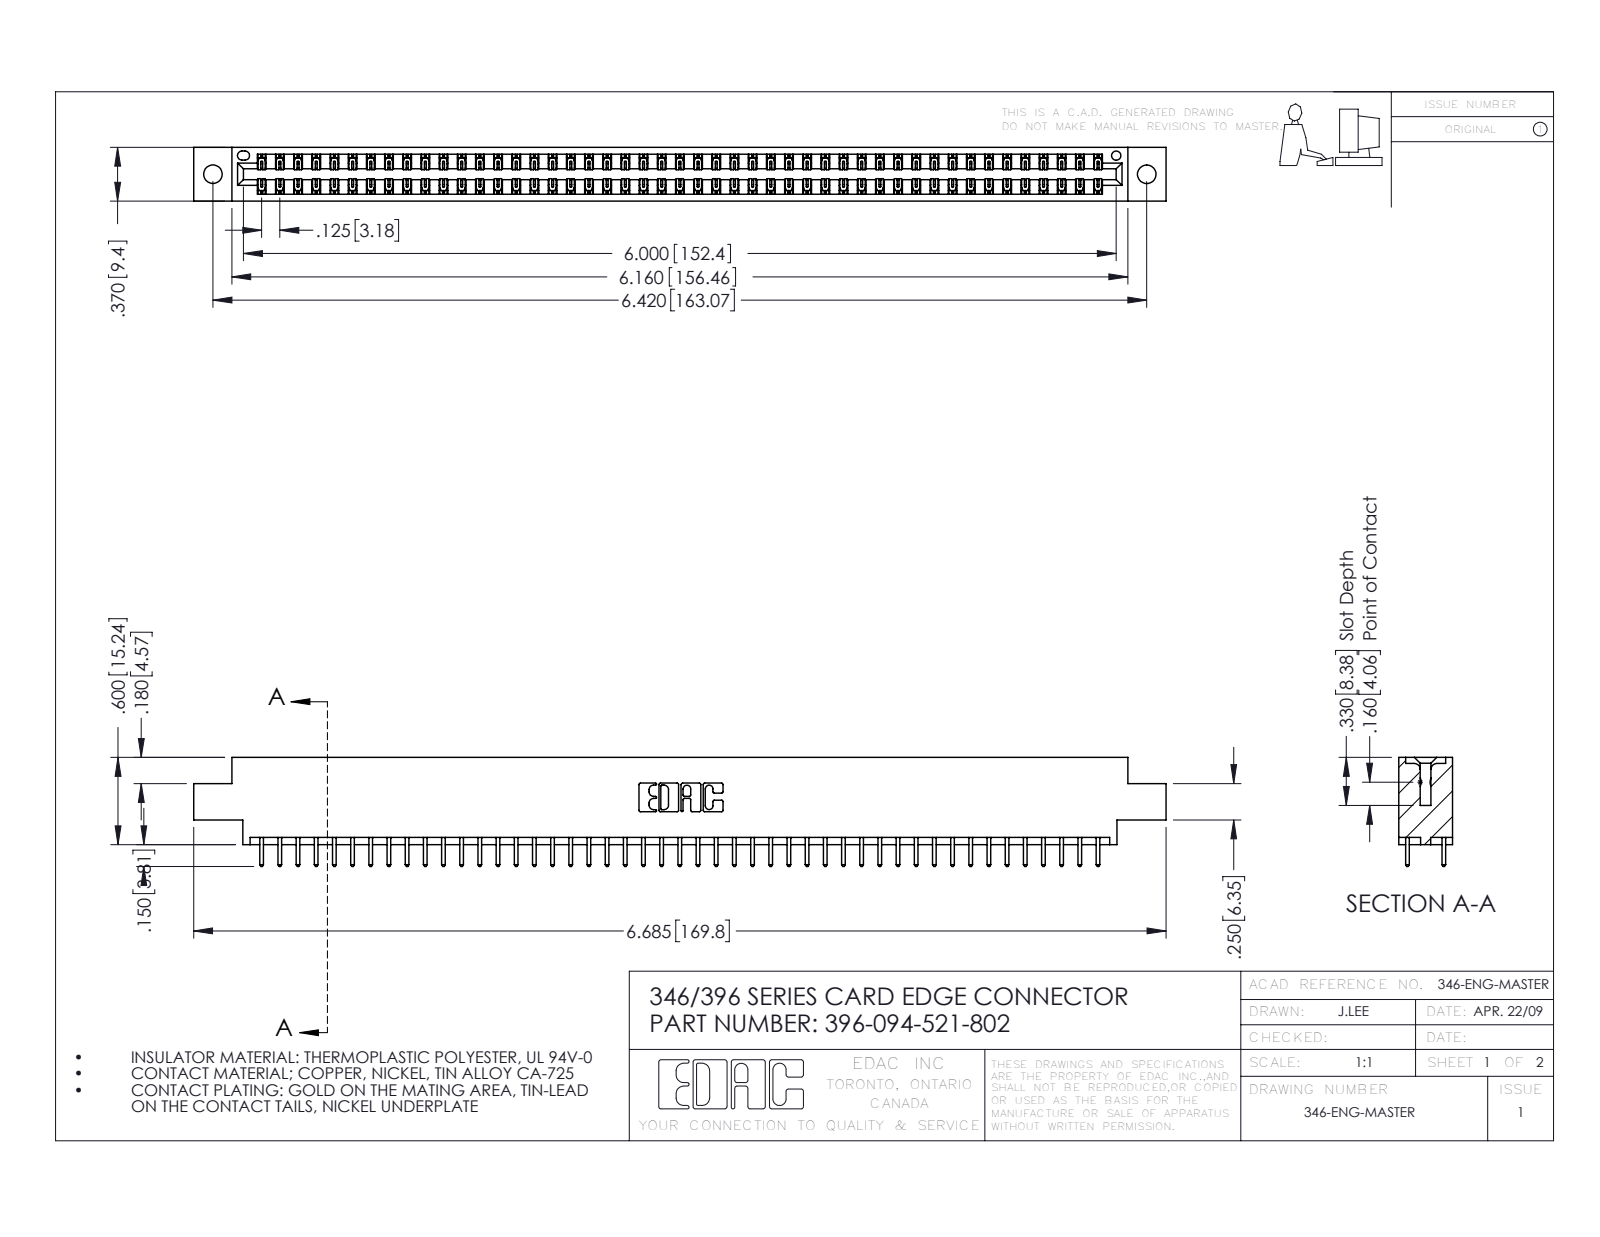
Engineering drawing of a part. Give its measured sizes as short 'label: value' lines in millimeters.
name: 346 Part_0.170 Offset - 0.128 Dia; 396-094-521-802; 345-292-001_345-293-121
written by: SolidWorks 2016 (CONFIG_CONTROL_DESIGN)
unit: mm
bodies: 95 solids, 5014 faces (3370 planar, 1644 cylindrical, 0 other)
size: 169.8 × 19.1 × 9.4
volume: 16 400 mm³; area: 22 230 mm²
holes: 2× ⌀3.3, 1× ⌀1.6
rounds: 141× R0.2, 94× R0.3, 22× R0.3, 6× R0.2, 6× R0.8, 3× R0.7, 2× R0.4, 2× R0.6
face distances: 1.2, 8.2, 9.4, 6.4, 1.8, 7.6, 0.6, 7, 3.8, 5.6
hole spacings: 6.2, 157.8, 163.1
